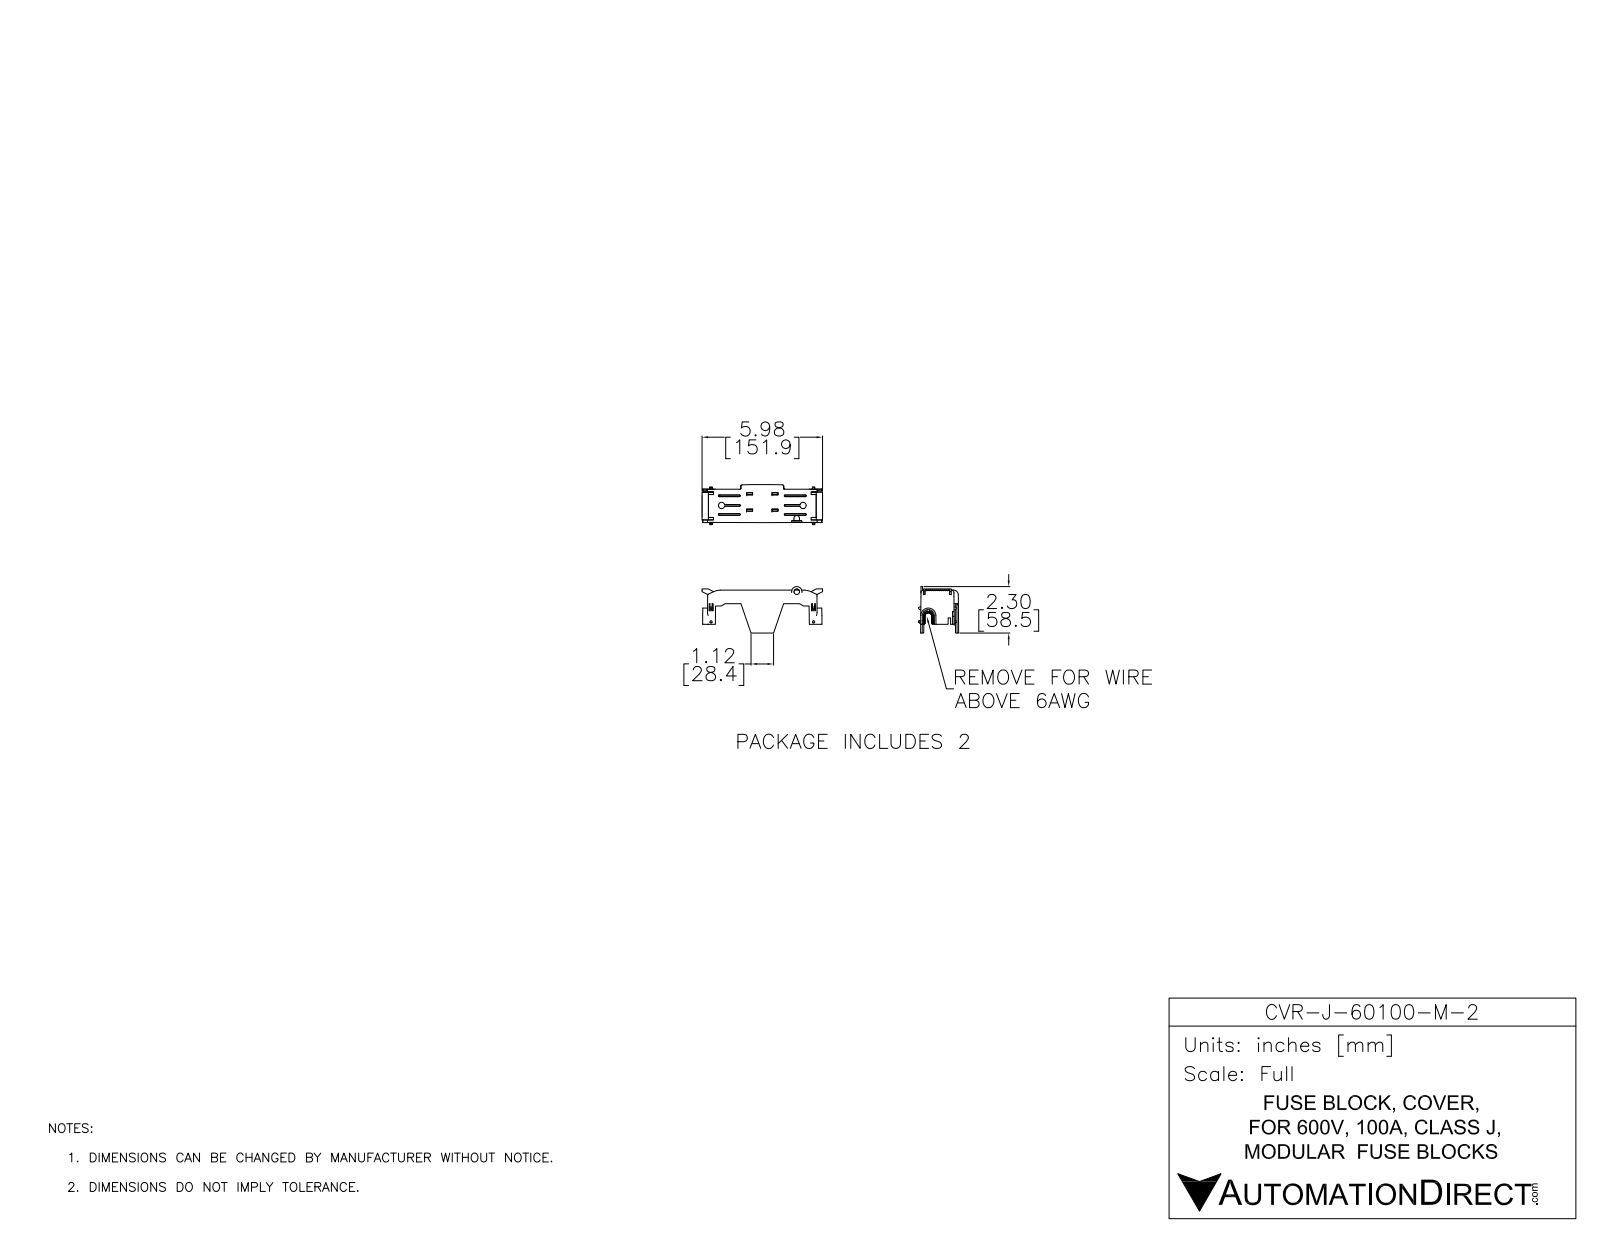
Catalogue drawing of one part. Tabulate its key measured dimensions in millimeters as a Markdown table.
| quantity | value |
| --- | --- |
| part name | CVR-J-60100-M-2 |
| STEP written by | SolidWorks 2017 (AUTOMOTIVE_DESIGN) |
| units | millimeters |
| bodies | 1 solid, 1410 faces (917 planar, 102 cylindrical, 391 other) |
| overall size | 151.9 × 58.5 × 50.4 |
| volume | 41 790 mm³ |
| surface area | 45 170 mm² |
| partial cylindrical surfaces (radius × count) | 1 × 19, 3 × 14, 0.8 × 6, 1.5 × 4, 0.3 × 2, 0.5 × 2, 3.5 × 2, 4.3 × 2 |
| main face-to-face distances | 2, 5.5, 3.5, 7.5, 3, 8.8, 5, 6, 3.6, 1.5 |
